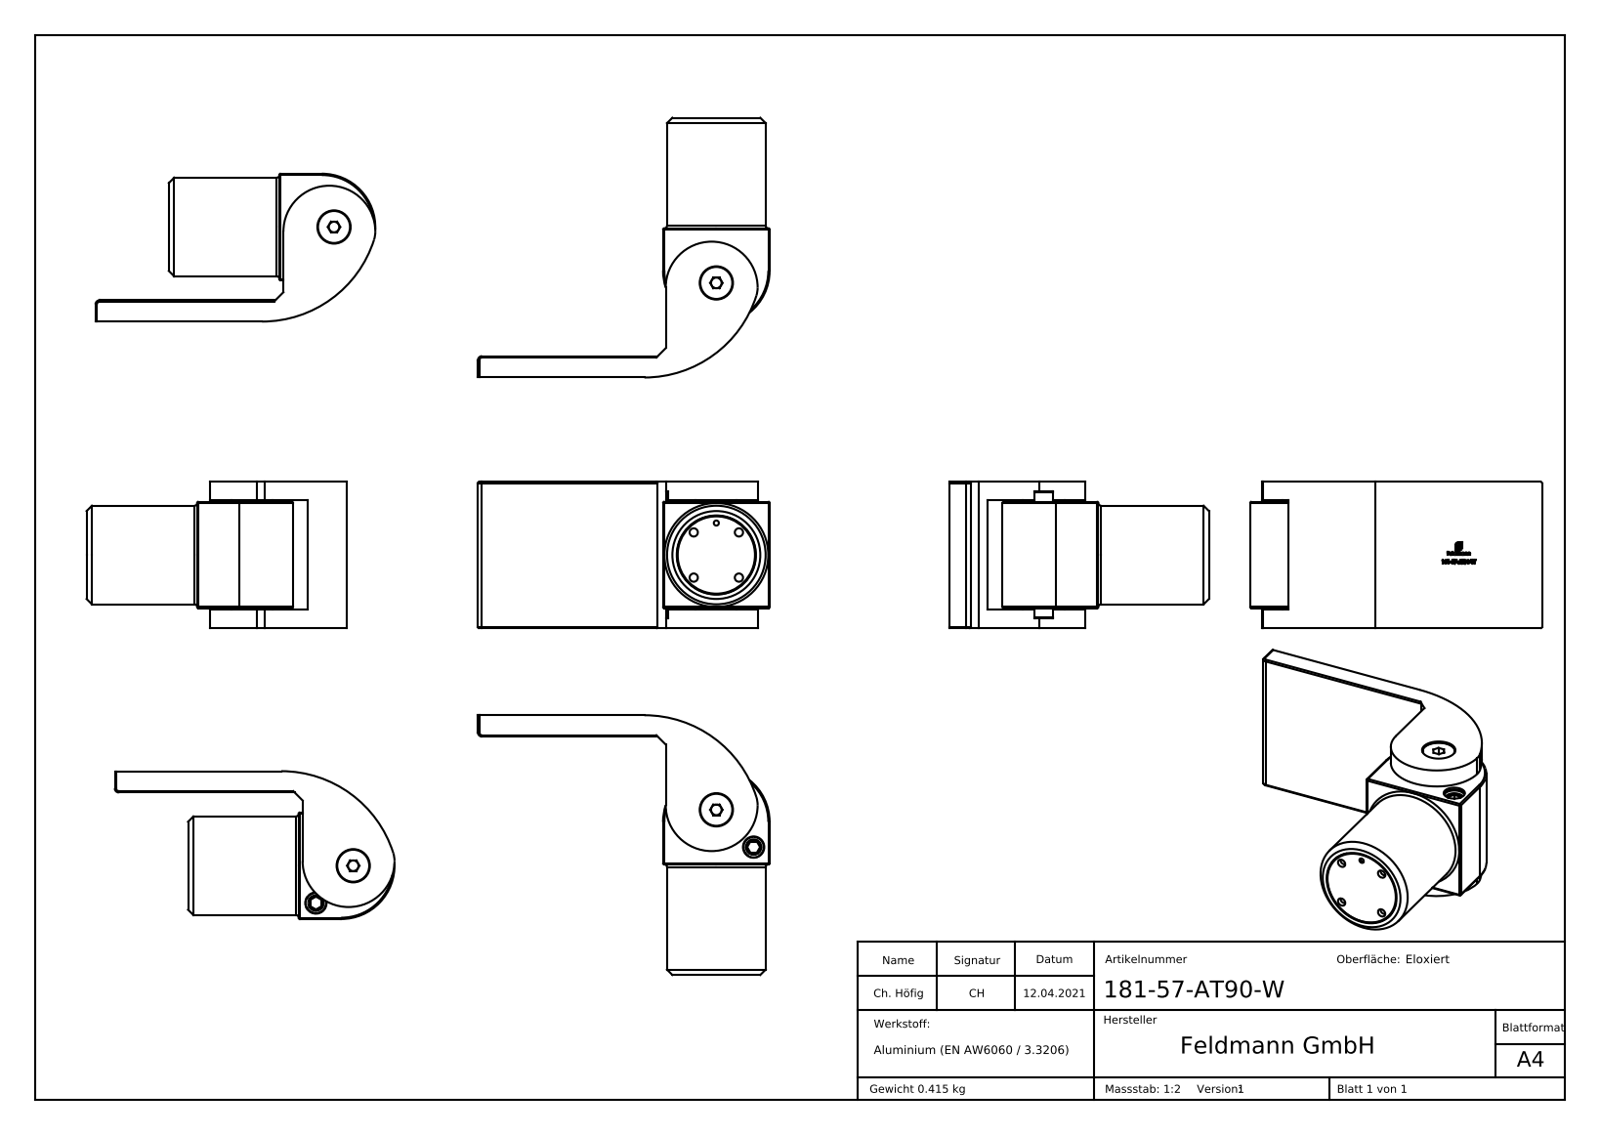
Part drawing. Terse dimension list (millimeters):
name: DIN-7991 M3-M10; Teil2; Teil1; 181-57-AT90-W (+3 more)
written by: SolidWorks 2018 (CONFIG_CONTROL_DESIGN)
unit: mm
bodies: 5 solids, 528 faces (271 planar, 82 cylindrical, 175 other)
size: 109.5 × 97.5 × 55
volume: 151 846 mm³; area: 33 773 mm²
holes: 4× ⌀3.1, 1× ⌀1.9, 1× ⌀5, 1× ⌀6.5, 1× ⌀8, 1× ⌀12.5, 1× ⌀15.7, 1× ⌀24, 1× ⌀29.7
bosses: 1× ⌀37, 1× ⌀29.5, 1× ⌀26, 1× ⌀23.6, 1× ⌀15.5, 1× ⌀12, 1× ⌀7.8, 1× ⌀6
rounds: 12× R0.5, 1× R1.5, 1× R10, 1× R17.25, 1× R20, 1× R44.11
face distances: 8, 48, 7, 55, 47.5, 0.5, 7.5, 40.5, 40, 14.5
hole spacings: 12.01, 16.98, 9.19, 22.18, 24.01, 12, 19.8
